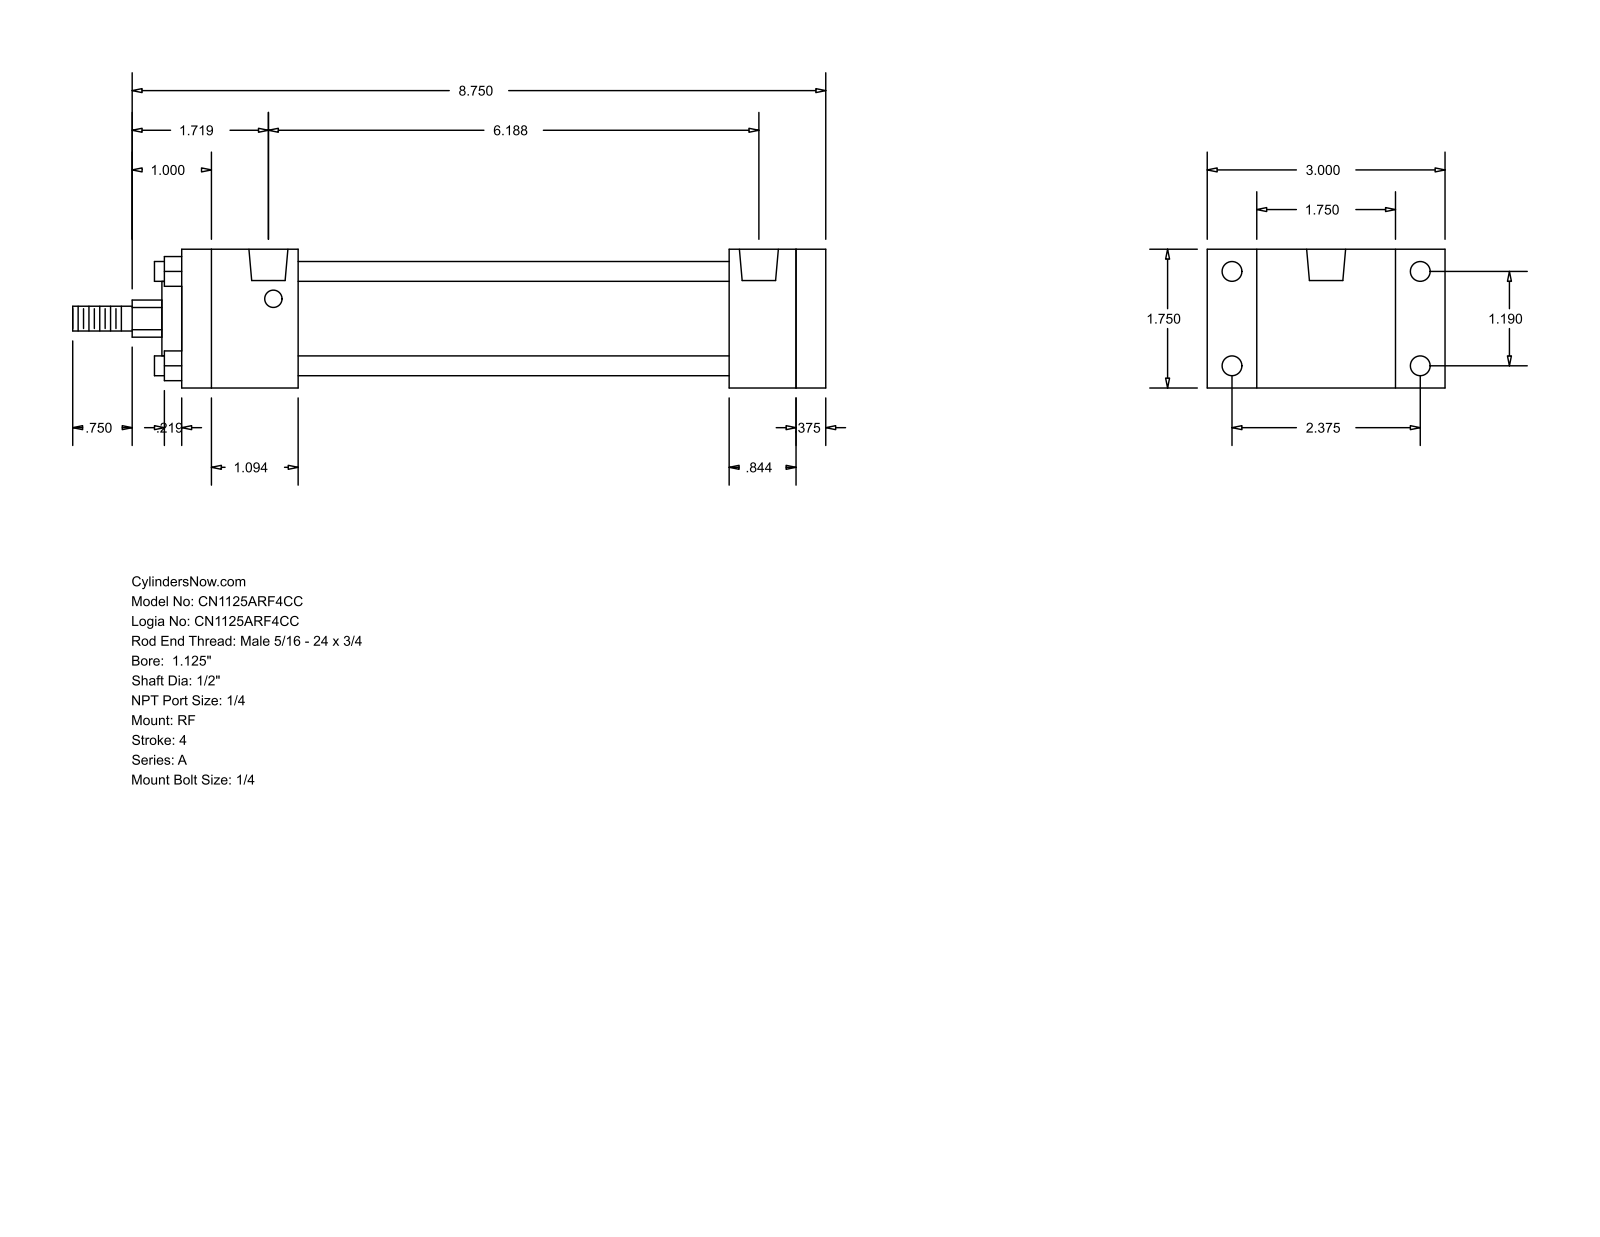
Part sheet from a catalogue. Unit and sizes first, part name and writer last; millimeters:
Units: millimetres
Overall size (bounding box): 241.3 × 76.2 × 44.45
Round holes (diameter × count): ⌀5.56 ×4, ⌀6.35 ×4, ⌀12.49 ×2
Round bosses / shafts (diameter × count): ⌀6.35 ×4, ⌀31.88 ×1, ⌀23.81 ×1, ⌀12.7 ×1, ⌀7.94 ×1
Partial cylindrical surfaces — rounded edges, fillets, slot ends (radius × count): R5.94 ×1
Main face-to-face distances: 44.46, 9.53, 206.37, 196.84, 37.3, 175.41, 138.11, 159.54, 169.07, 21.43
Hole centre spacings: 30.22, 60.32, 67.47, 153.99, 1.58, 1.59, 155.57, 155.58
Bodies: 0 solids, 92 faces (64 planar, 28 cylindrical, 0 other)
Part name (STEP PRODUCT): A_RF__0112_0.5
STEP written by: GSSL Pune (CONFIG_CONTROL_DESIGN)
